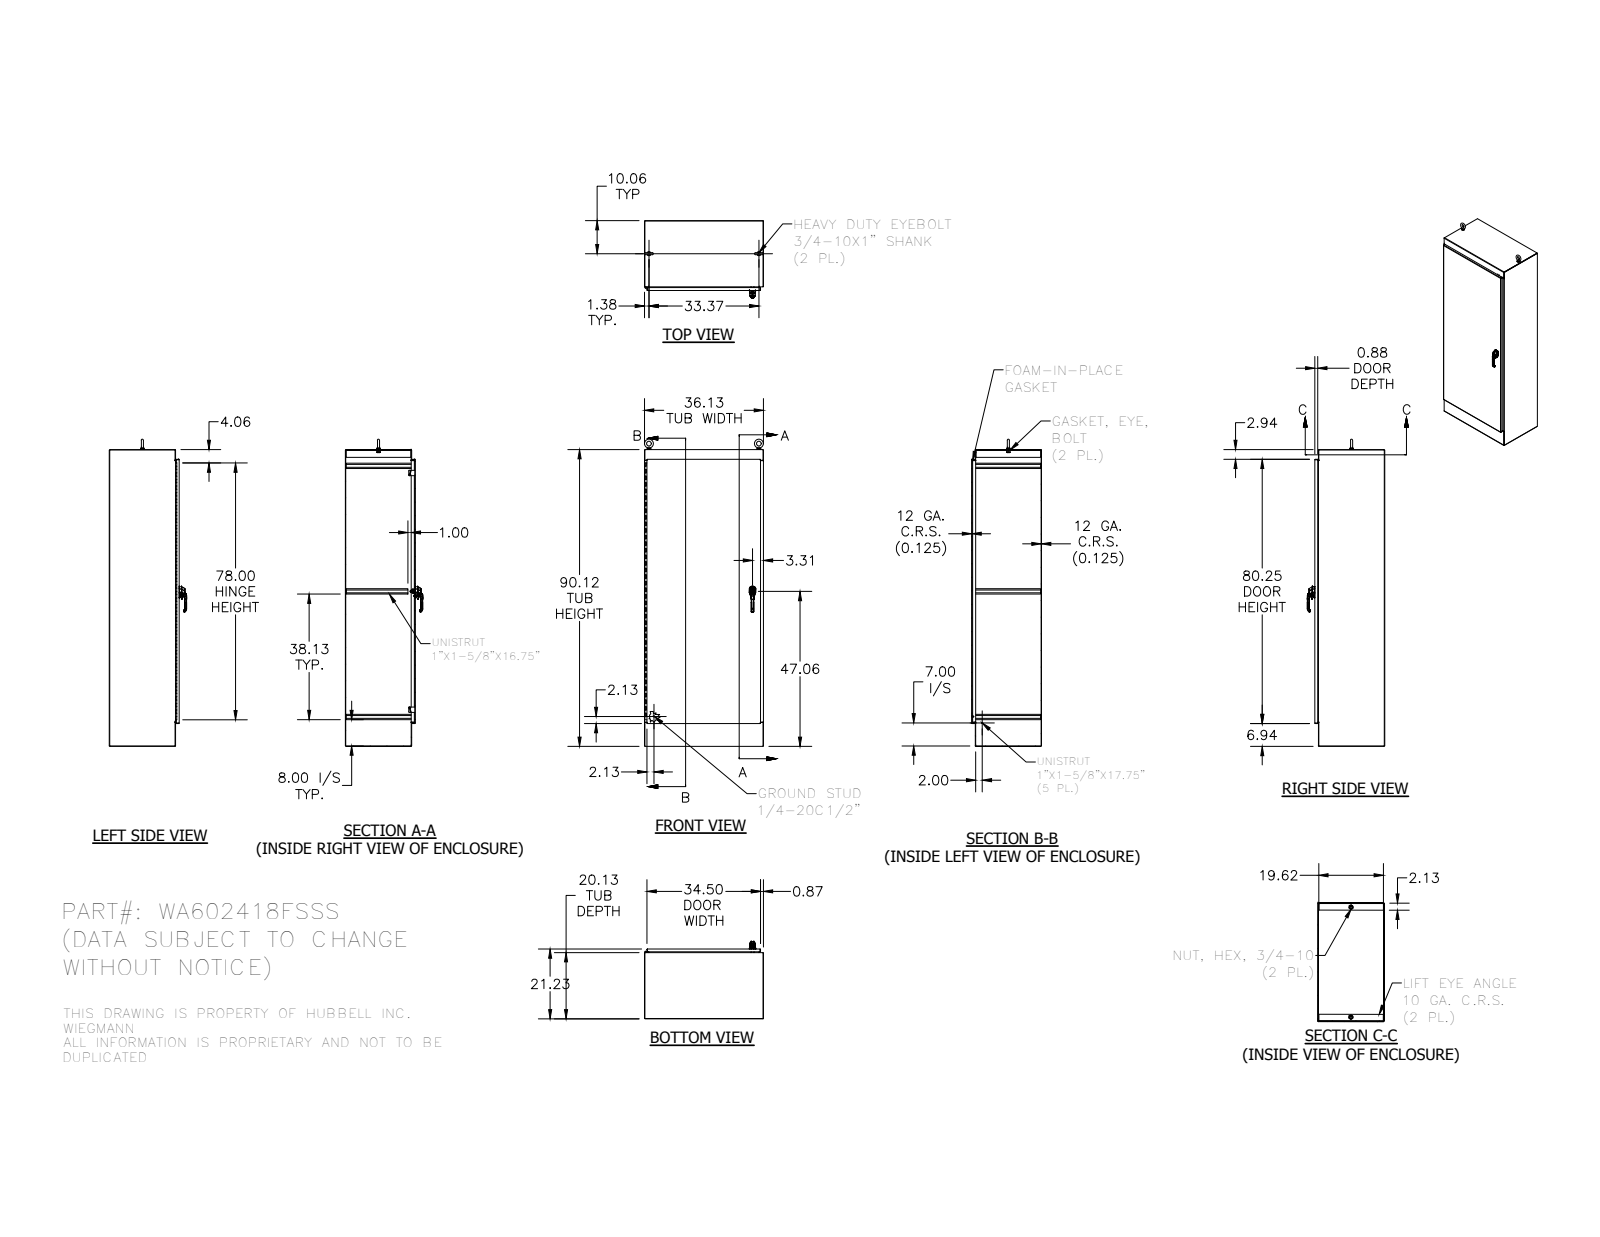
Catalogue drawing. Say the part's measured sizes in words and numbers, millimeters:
The part is named "WA9036FSFB; WA9020FSLS; WA9020FSRS; WA3620FSBTM-10GA (+8 more)". Its 3-D file was written by "Autodesk Inventor 2014 (AUTOMOTIVE_DESIGN)". It is 47 solids with 2834 faces: 1207 planar, 980 cylindrical and 647 other. Overall it measures 2368.49 by 917.58 by 596.35 millimeters. Its volume is 26 060 000 cubic millimeters and its surface area 16 720 000 square millimeters. Round holes: 8 of diameter 7.02, 8 of diameter 9.52, 4 of diameter 5.08, 3 of diameter 5.4, 3 of diameter 7.11, 2 of diameter 8, 2 of diameter 10.2, 2 of diameter 10.33, 2 of diameter 10.5, 2 of diameter 16.31, 2 of diameter 20.64, 1 of diameter 3.1. Round bosses or shafts: 2 of diameter 31.75, 2 of diameter 28.45, 2 of diameter 19.05, 2 of diameter 13.5, 2 of diameter 13.37, 2 of diameter 11.05, 2 of diameter 8.56, 2 of diameter 6.35. Partial cylindrical surfaces (rounded edges, fillets, slot ends): 178 of radius 0.5, 100 of radius 0.3, 23 of radius 0.47, 16 of radius 0.25, 16 of radius 3.17, 14 of radius 0.79, 14 of radius 2, 14 of radius 3.97. The main face-to-face distances are 3.18, 914.4, 3.17, 532.88, 536.06, 539.23, 536.05, 911.22, 917.58, 2286. The hole center spacings are 220.13, 660.4, 440.27, 880.53, 9.66, 9.7, 9.71, 19.36.
